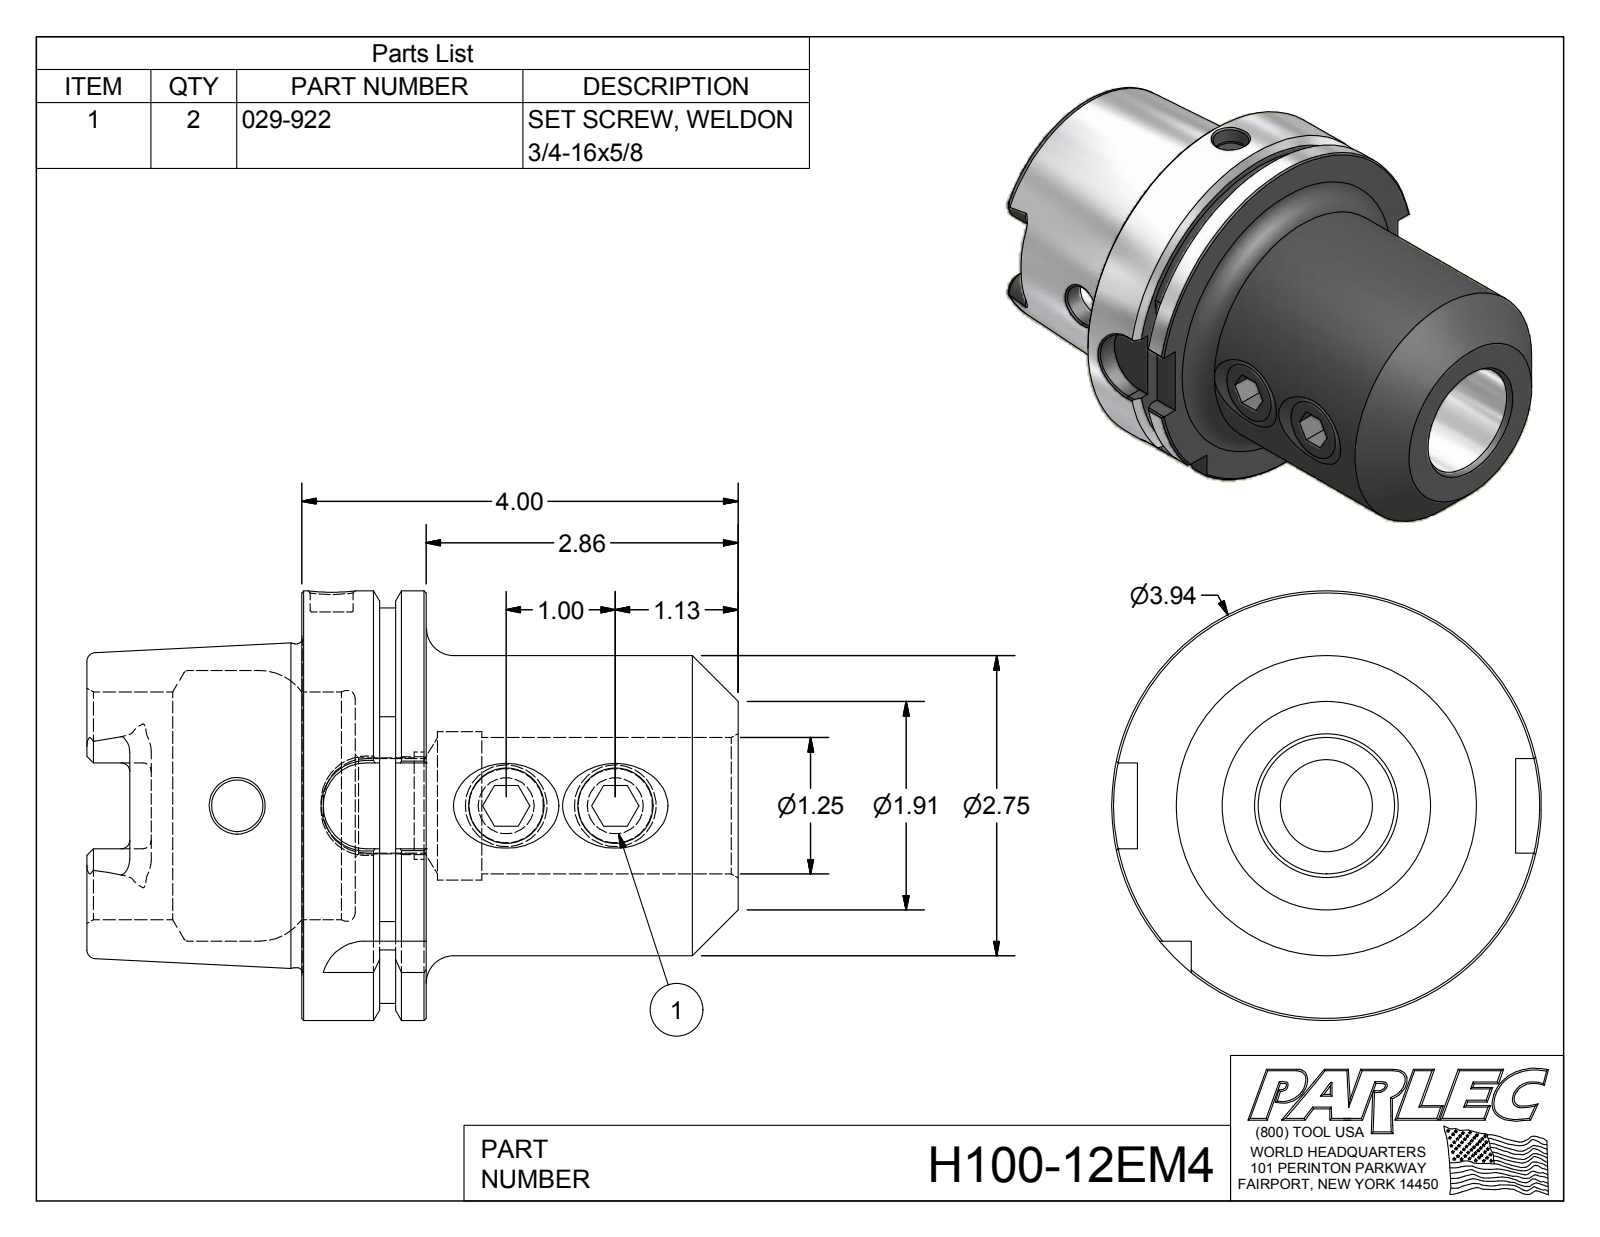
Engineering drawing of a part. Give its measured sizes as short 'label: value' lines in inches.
name: H100-12EM4; 029-922
written by: Autodesk Inventor 2012 (AUTOMOTIVE_DESIGN)
unit: in
bodies: 3 solids, 153 faces (62 planar, 37 cylindrical, 54 other)
size: 5.969 × 3.937 × 3.937
volume: 28.18 in³; area: 116.2 in²
holes: 2× ⌀0.682, 1× ⌀0.394, 1× ⌀0.472, 1× ⌀0.881, 1× ⌀0.985, 1× ⌀1.25, 1× ⌀1.36, 1× ⌀2.087, 1× ⌀2.48
bosses: 2× ⌀0.75, 1× ⌀3.937, 1× ⌀2.967, 1× ⌀2.75
rounds: 6× R0.079, 4× R0.192, 4× R0.394, 1× R1.811
face distances: 1.142, 0.492, 0.65, 4, 3.508, 2.858, 1.969, 2.461, 3.11, 5.969
hole spacings: 1, 2.466, 3.466
